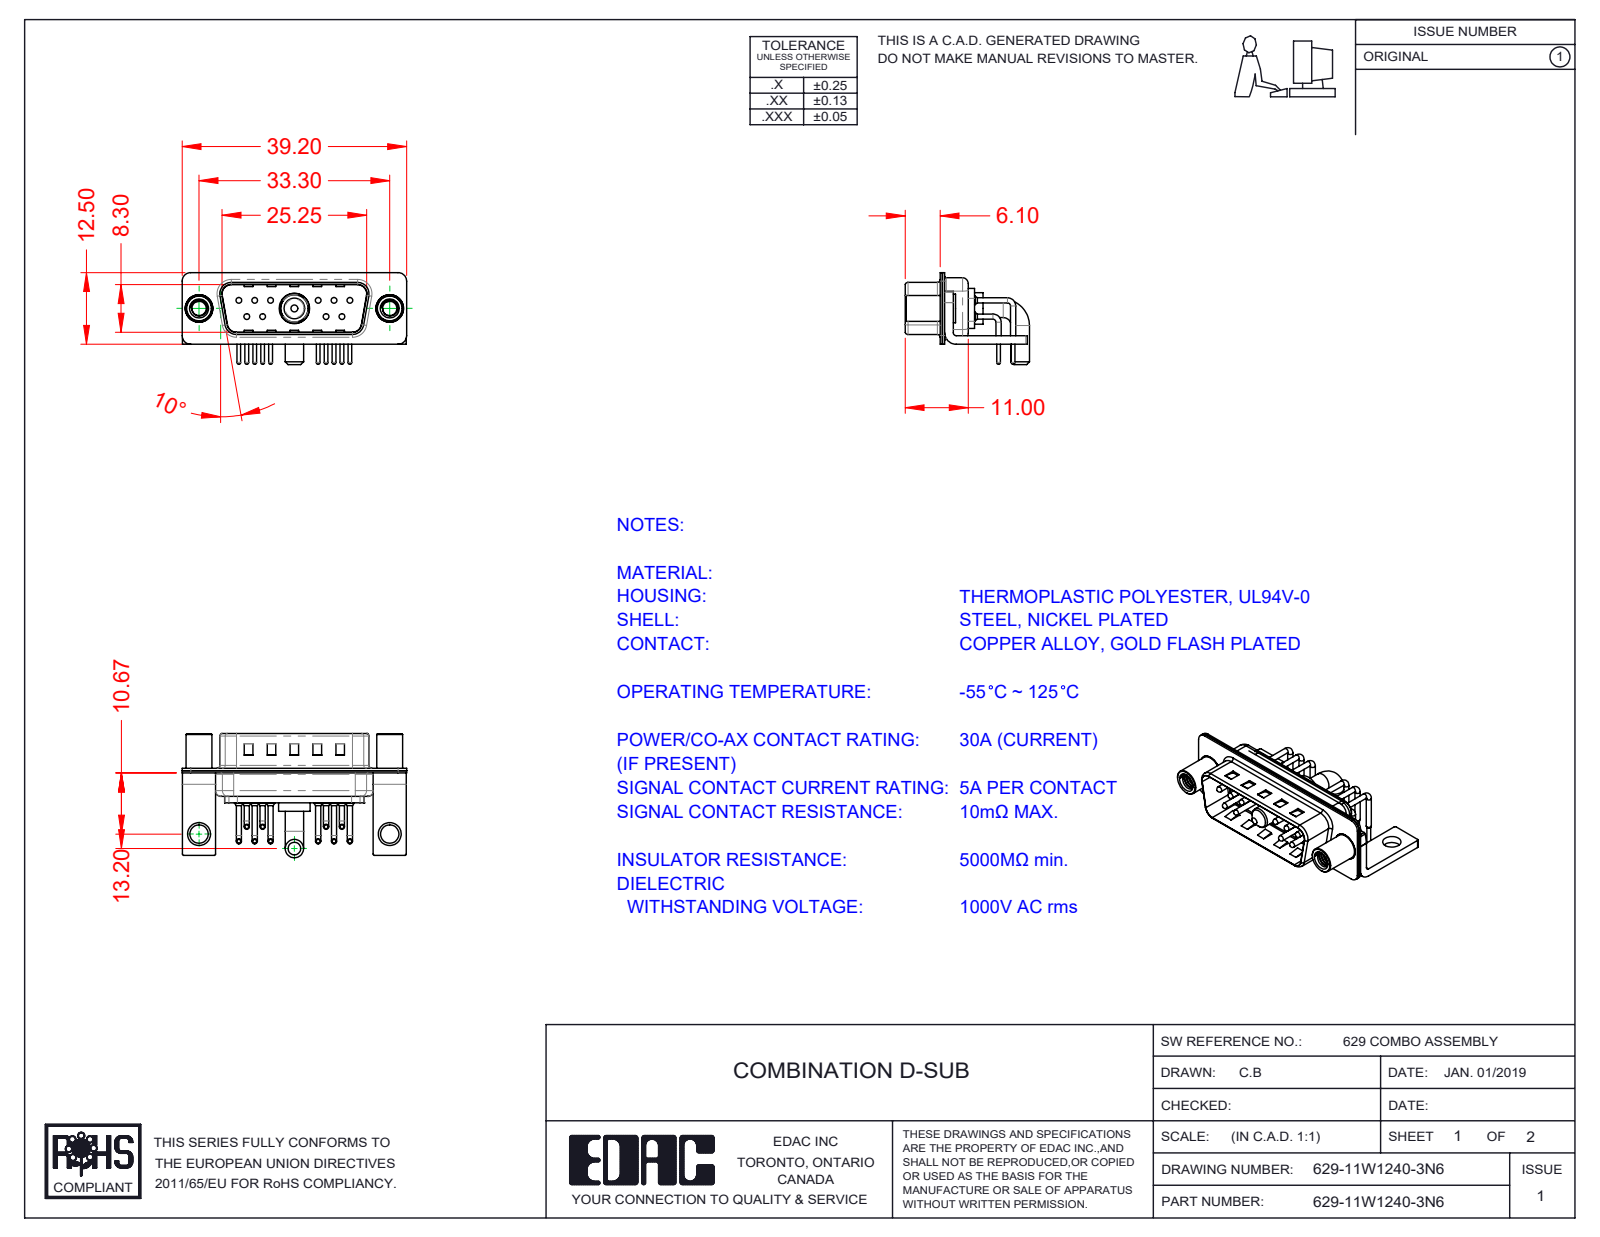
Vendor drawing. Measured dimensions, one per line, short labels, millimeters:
name: 629-11W1240-3N6; 629Combo Shell Rear_15 Contacts; Power Pin_30A RA; 629Combo Shell Front_15 Contacts (+5 more)
written by: SolidWorks 2020 (CONFIG_CONTROL_DESIGN)
unit: mm
bodies: 19 solids, 1594 faces (820 planar, 590 cylindrical, 184 other)
size: 39.2 × 21.7 × 16.05
volume: 2 475 mm³; area: 6 176 mm²
holes: 10× ⌀0.75, 10× ⌀1.6, 10× ⌀2, 2× ⌀2.5, 2× ⌀3.2, 2× ⌀4, 2× ⌀4.8, 1× ⌀4.85, 1× ⌀5.3
bosses: 20× ⌀0.9, 10× ⌀1.5, 10× ⌀1, 10× ⌀0.65, 2× ⌀5, 2× ⌀4.9, 2× ⌀4.5, 2× ⌀3.2
rounds: 16× R0.25, 16× R1.5, 13× R2, 10× R1.01, 9× R0.5, 8× R1.6, 7× R1, 4× R0.6
face distances: 0.4, 0.8, 1.5, 9.5, 9.1, 8.7, 9.9, 0.6, 1.9, 5.2
hole spacings: 3.16, 2.77, 13.85, 11.08, 16.62, 5.03, 5.04, 5.54
